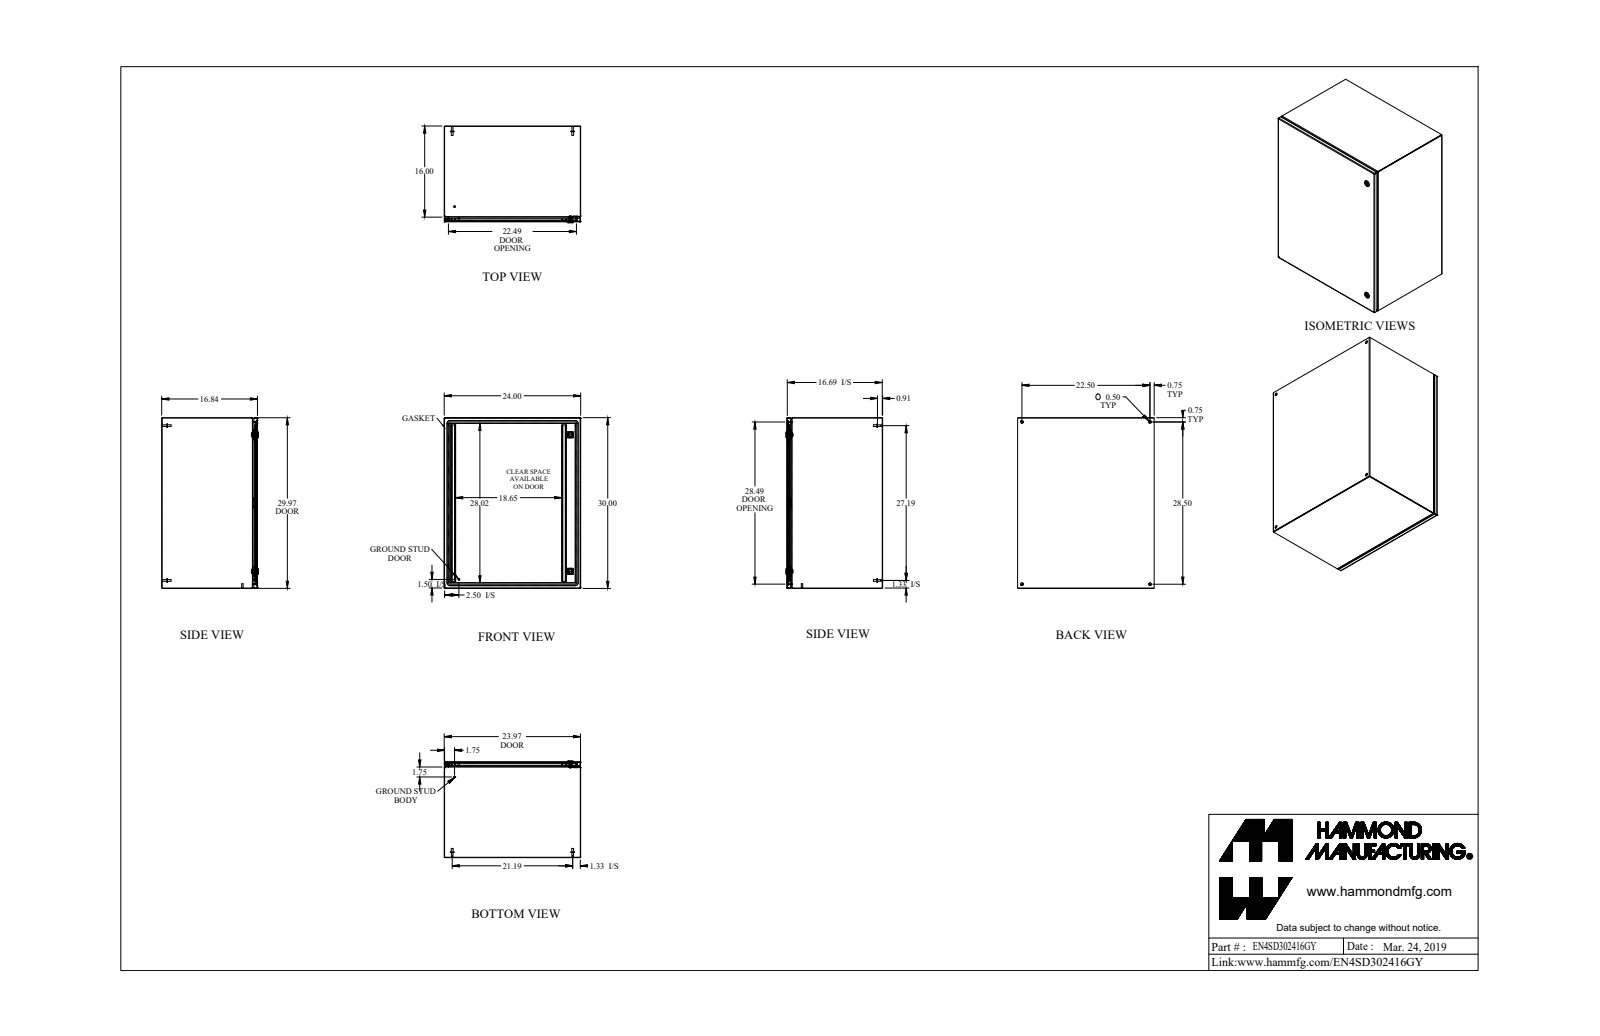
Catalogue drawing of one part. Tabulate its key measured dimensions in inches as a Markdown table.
| quantity | value |
| --- | --- |
| part name | EN4SD302416GY |
| STEP written by | SolidWorks 2019 (AUTOMOTIVE_DESIGN) |
| units | inches |
| bodies | 33 solids, 826 faces (399 planar, 275 cylindrical, 152 other) |
| overall size | 30 × 24 × 16.997 |
| volume | 257.4 in³ |
| surface area | 7 217 in² |
| round holes (diameter × count) | 0.5 × 4, 0.232 × 2, 0.625 × 2, 0.785 × 2, 0.172 × 1, 0.24 × 1, 0.242 × 1 |
| round bosses / shafts (diameter × count) | 0.625 × 4, 0.313 × 4, 0.27 × 4, 1.1 × 2, 0.525 × 2, 0.281 × 2, 0.25 × 2, 0.455 × 1 |
| partial cylindrical surfaces (radius × count) | 0.036 × 14, 0.108 × 14, 0.043 × 12, 0.081 × 12, 0.312 × 12, 0.006 × 6, 0.062 × 6, 0.125 × 4 |
| main face-to-face distances | 0.072, 16.765, 23.928, 29.928, 16.693, 16.837, 23.856, 24, 29.856, 30 |
| hole center spacings | 22.5, 28.5, 36.311, 2.493, 2.494, 21.545, 21.545, 23.999 |
